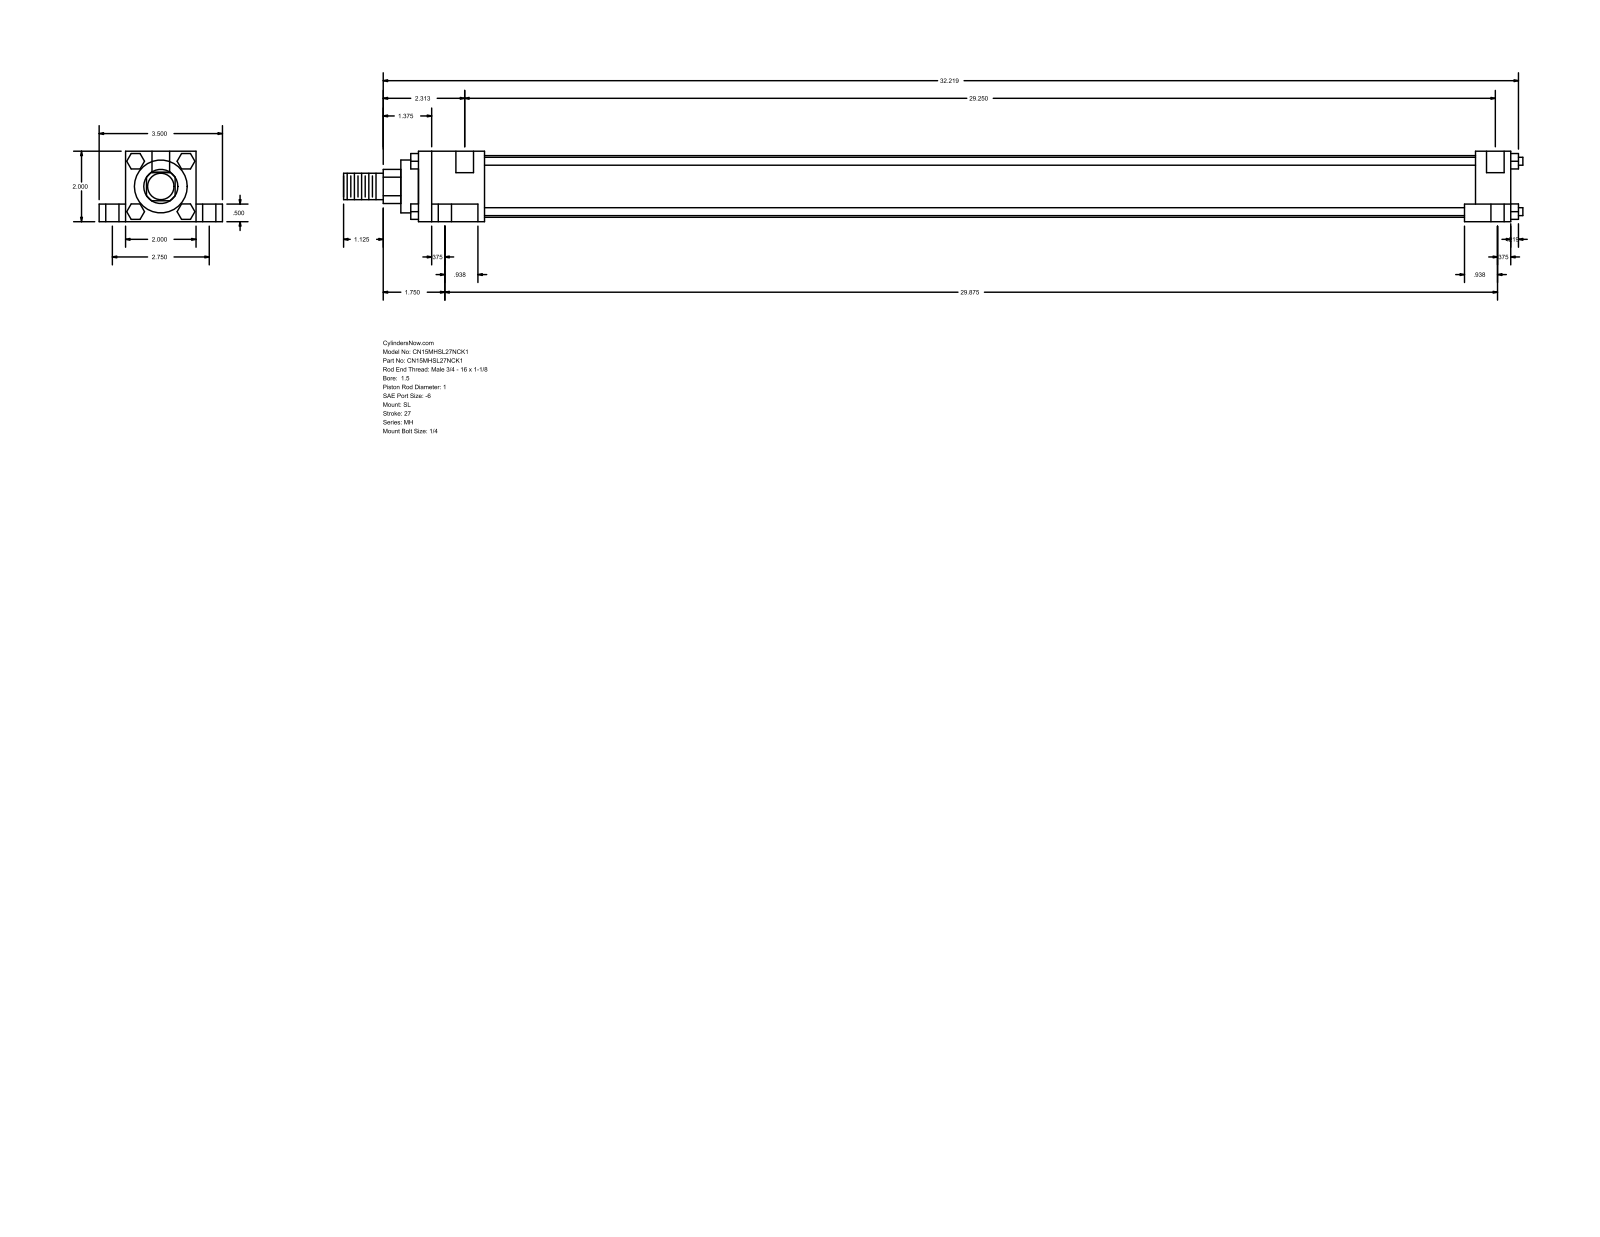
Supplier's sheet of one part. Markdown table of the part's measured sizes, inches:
| quantity | value |
| --- | --- |
| part name | MH_SL__0150_1 |
| STEP written by | GSSL Pune (CONFIG_CONTROL_DESIGN) |
| units | inches |
| bodies | 0 solids, 148 faces (112 planar, 36 cylindrical, 0 other) |
| overall size | 33.469 × 3.5 × 2 |
| round holes (diameter × count) | 0.219 × 4, 0.375 × 4, 0.625 × 4, 0.5 × 2 |
| round bosses / shafts (diameter × count) | 0.225 × 4, 1.75 × 1, 1.5 × 1, 1 × 1, 0.75 × 1 |
| partial cylindrical surfaces (radius × count) | 0.484 × 1 |
| main face-to-face distances | 2, 0.5, 1.5, 0.75, 2.75, 31, 1, 0.375, 1.313, 29.313 |
| hole center spacings | 1.376, 1.443, 1.485, 2.75, 29.344, 29.375, 29.469, 29.844 |
